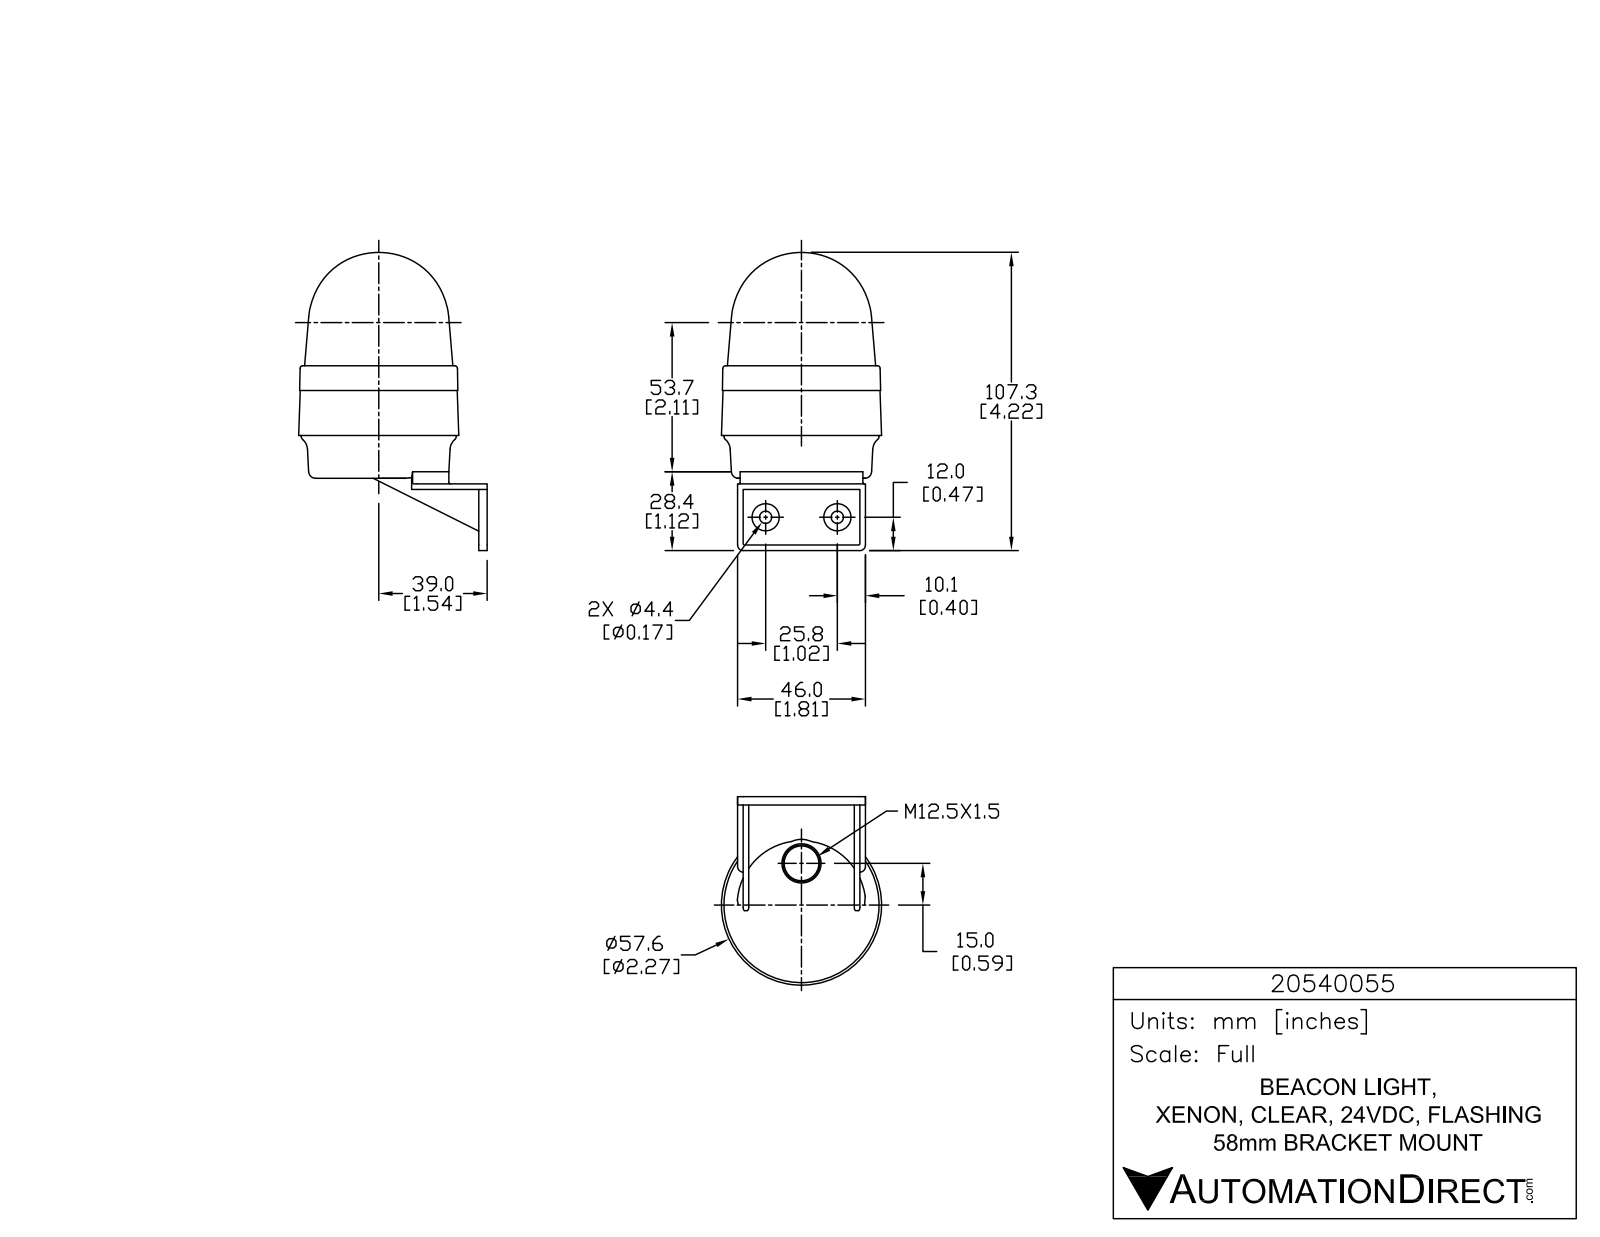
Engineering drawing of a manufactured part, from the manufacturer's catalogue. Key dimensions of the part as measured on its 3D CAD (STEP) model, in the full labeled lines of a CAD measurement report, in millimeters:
Part name (STEP PRODUCT): 20540055
STEP written by: SolidWorks 2015 (AUTOMOTIVE_DESIGN)
Units: millimetres
Bodies: 1 solid, 828 faces (551 planar, 179 cylindrical, 98 other)
Overall size (bounding box): 107.3 × 72.4 × 61.1
Volume: 168 300 mm³ · Surface area: 21 540 mm²
Round holes (diameter × count): ⌀1 ×3, ⌀4.4 ×2
Round bosses / shafts (diameter × count): ⌀5.7 ×3, ⌀1.4 ×3, ⌀9.8 ×2, ⌀55.8 ×1
Partial cylindrical surfaces — rounded edges, fillets, slot ends (radius × count): R0.2 ×6, R0.2 ×6, R0.2 ×6, R0.5 ×6, R3.3 ×6, R2 ×4, R0.1 ×3, R0.1 ×3
Main face-to-face distances: 2, 4, 40, 42, 1, 3, 38, 22, 24, 19.4
Hole centre spacings: 25.8
